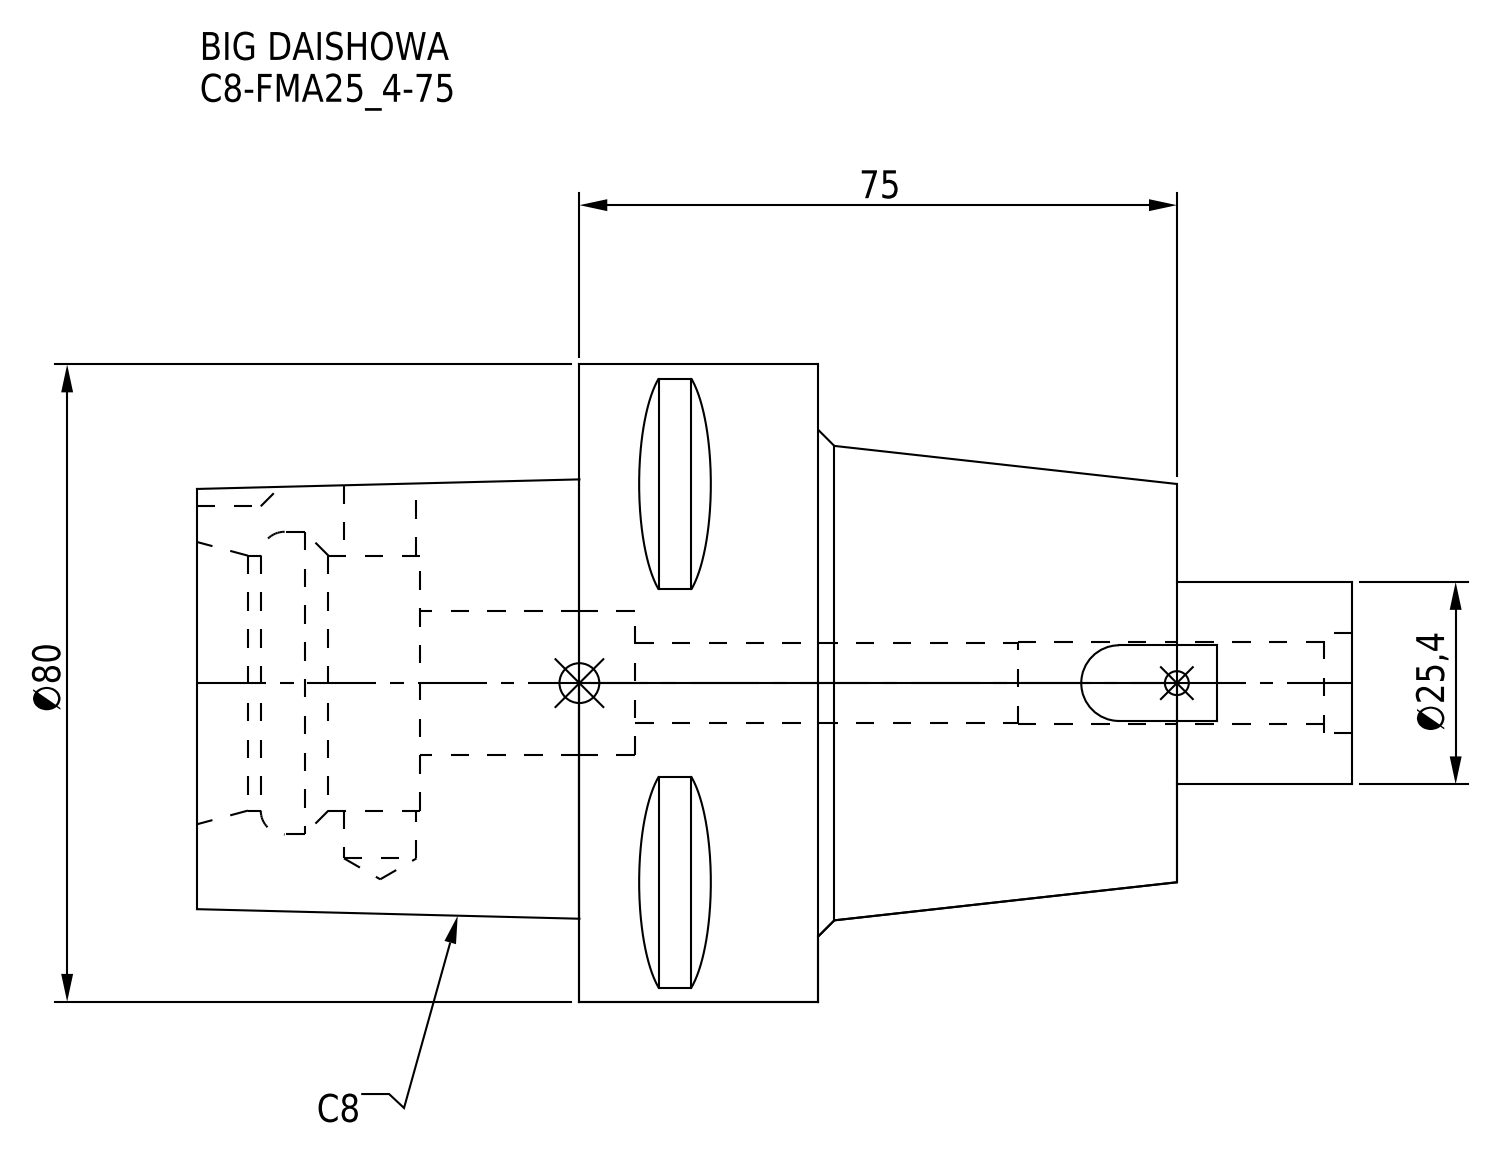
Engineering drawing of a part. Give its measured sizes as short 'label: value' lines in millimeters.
name: C8-FMA25_4-75
written by: CREO PARAMETRIC BY PTC INC, 2016380 (AUTOMOTIVE_DESIGN)
unit: mm
bodies: 1 solid, 78 faces (41 planar, 23 cylindrical, 14 other)
size: 145 × 80 × 80
volume: 335 542 mm³; area: 42 718 mm²
holes: 1× ⌀9.1, 1× ⌀10, 1× ⌀10.25, 1× ⌀12.5, 1× ⌀18, 1× ⌀32, 1× ⌀38
bosses: 1× ⌀80, 1× ⌀25.4
rounds: 1× R6
face distances: 30, 75, 45, 48, 123, 78, 50, 20, 95, 28
